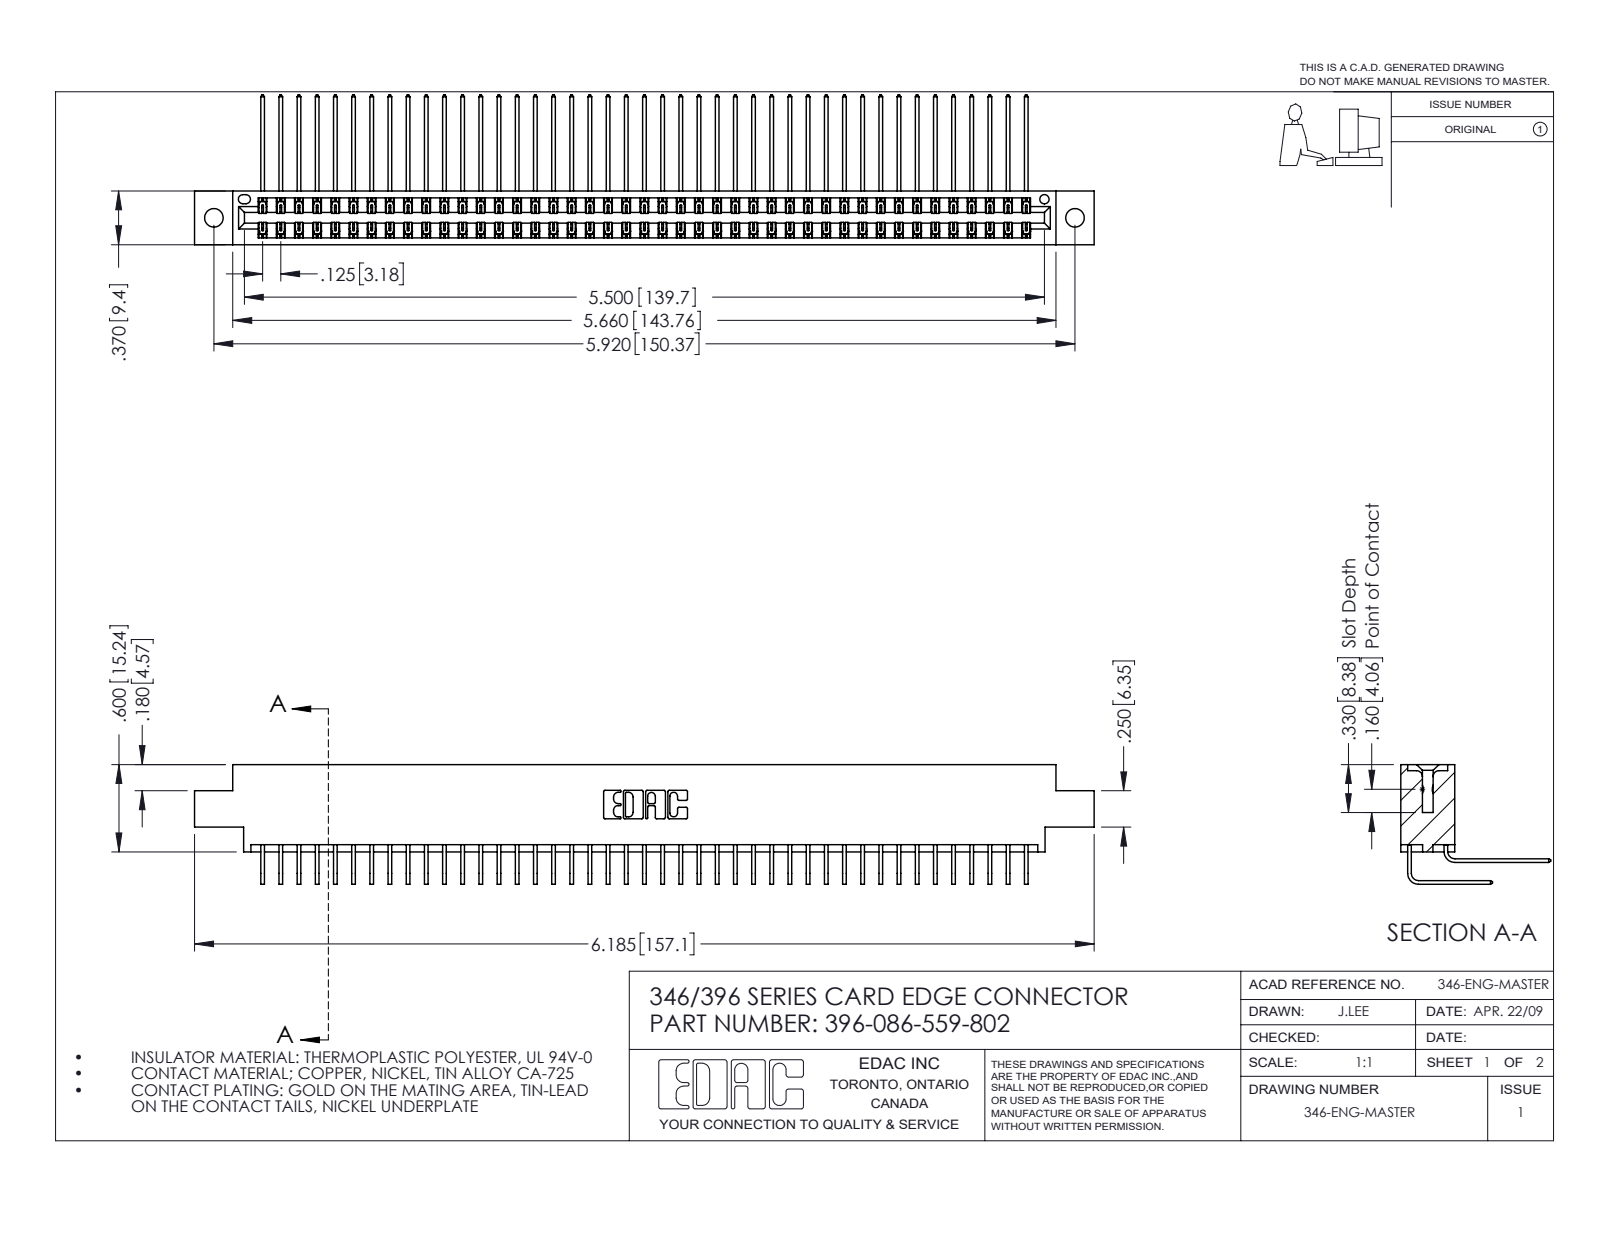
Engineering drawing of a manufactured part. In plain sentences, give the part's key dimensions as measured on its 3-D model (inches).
The part is named "396-086-559-802; 346 Part_0.170 Offset - 0.128 Dia; 345-292-001_558 559 Tail - 1; 345-292-001_559 Tail - 2". Its 3-D file was written by "SolidWorks 2016 (CONFIG_CONTROL_DESIGN)". It is 87 solids with 4770 faces: 3262 planar, 1508 cylindrical and 0 other. Overall it measures 6.185 by 1.03 by 0.823 inches. Its volume is 0.954 cubic inches and its surface area 36.88 square inches. Round holes: 2 of diameter 0.128, 1 of diameter 0.064. Partial cylindrical surfaces (rounded edges, fillets, slot ends): 129 of radius 0.006, 22 of radius 0.01, 6 of radius 0.007, 6 of radius 0.031, 3 of radius 0.026, 2 of radius 0.014, 2 of radius 0.022, 2 of radius 0.024. The main face-to-face distances are 0.048, 0.322, 0.025, 0.37, 0.25, 0.072, 0.298, 0.275, 0.148, 0.222. The hole center spacings are 0.246, 5.711, 5.92.
